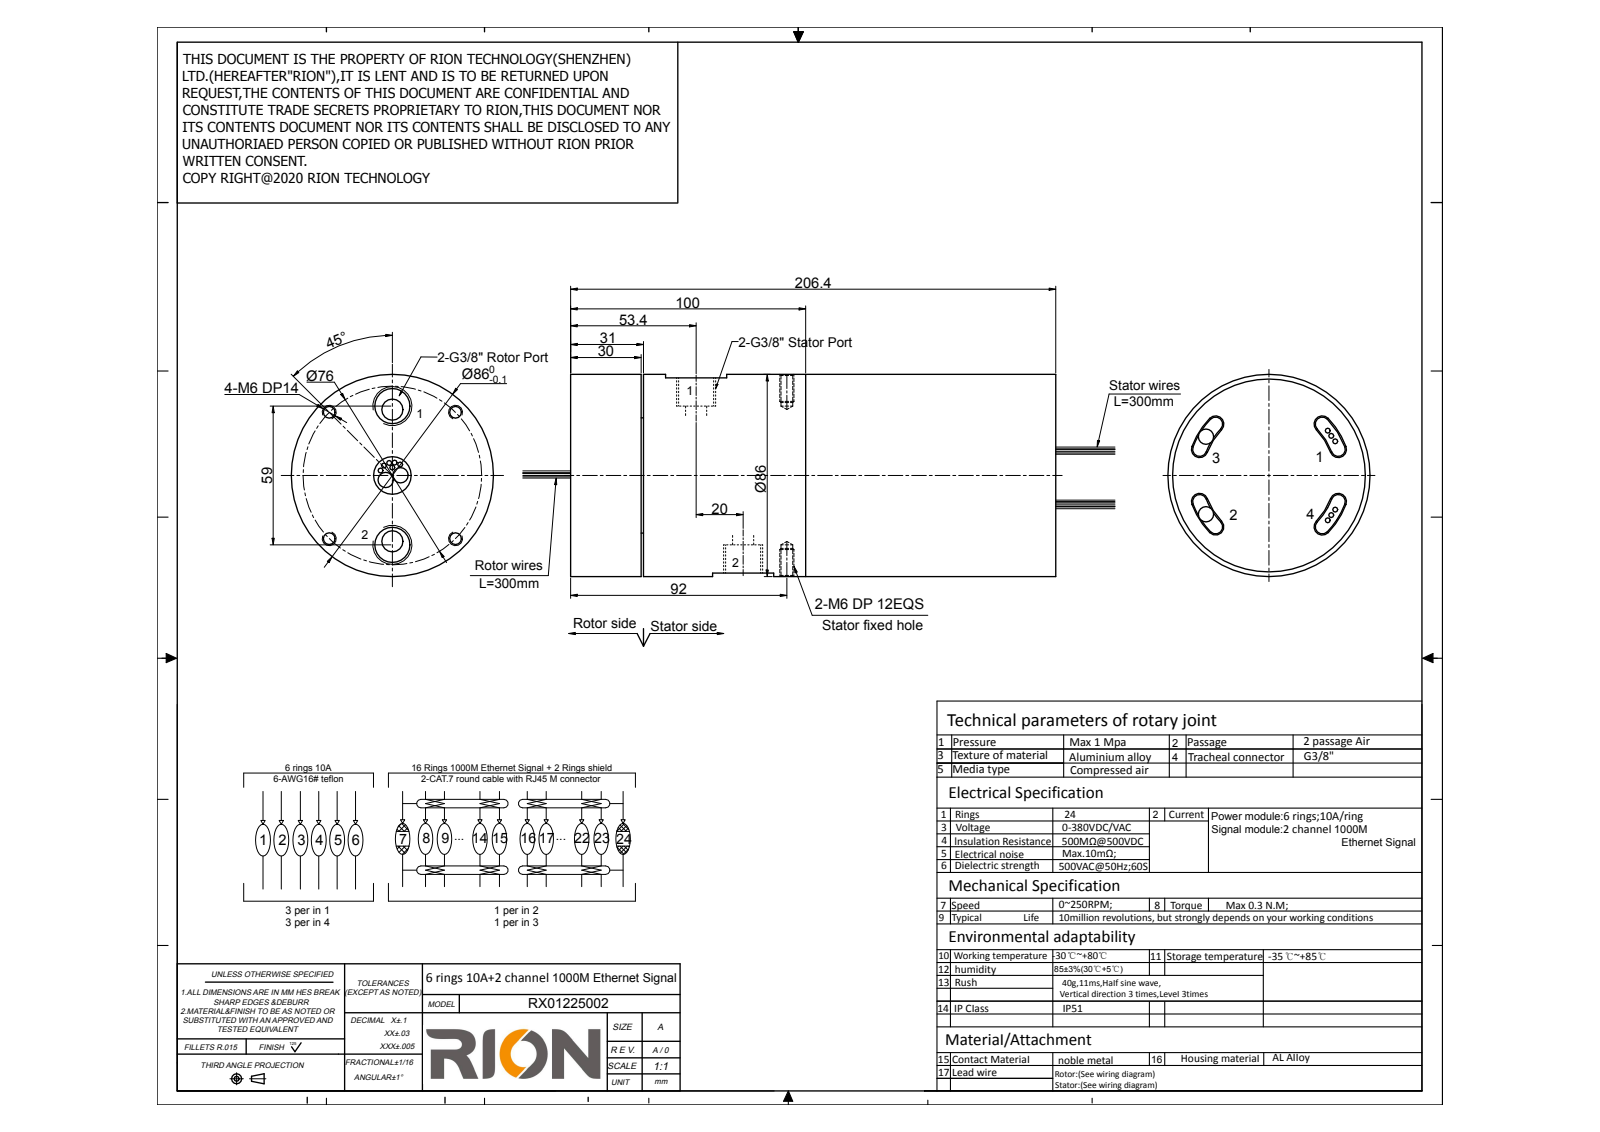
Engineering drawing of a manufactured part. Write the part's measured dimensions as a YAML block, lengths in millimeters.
part_name: "RX01225002"
step_written_by: "SolidWorks 2014 (CONFIG_CONTROL_DESIGN)"
units: millimeters
bodies: {solids: 1, faces: 201, planar: 47, cylindrical: 116, other: 38}
overall_size: [246.4, 86, 86]
volume: 1158000
surface_area: 95474
round_holes:
  - {diameter: 5, count: 9}
  - {diameter: 3.3, count: 5}
  - {diameter: 9, count: 4}
  - {diameter: 15.25, count: 4}
  - {diameter: 16, count: 1}
  - {diameter: 52, count: 1}
round_bosses_or_shafts:
  - {diameter: 2.1, count: 12}
  - {diameter: 6.5, count: 4}
  - {diameter: 86, count: 1}
  - {diameter: 49, count: 1}
  - {diameter: 40, count: 1}
partial_cylinders:
  - {radius: 3, count: 8}
  - {radius: 28.5, count: 1}
  - {radius: 34.5, count: 1}
face_to_face_distances: [206.4, 1, 30, 31, 176.4, 175.4, 69, 106.4, 100, 70]
hole_center_spacings: [38, 14.83, 15.58, 15.97, 26.92, 27, 27.36, 39.21]
